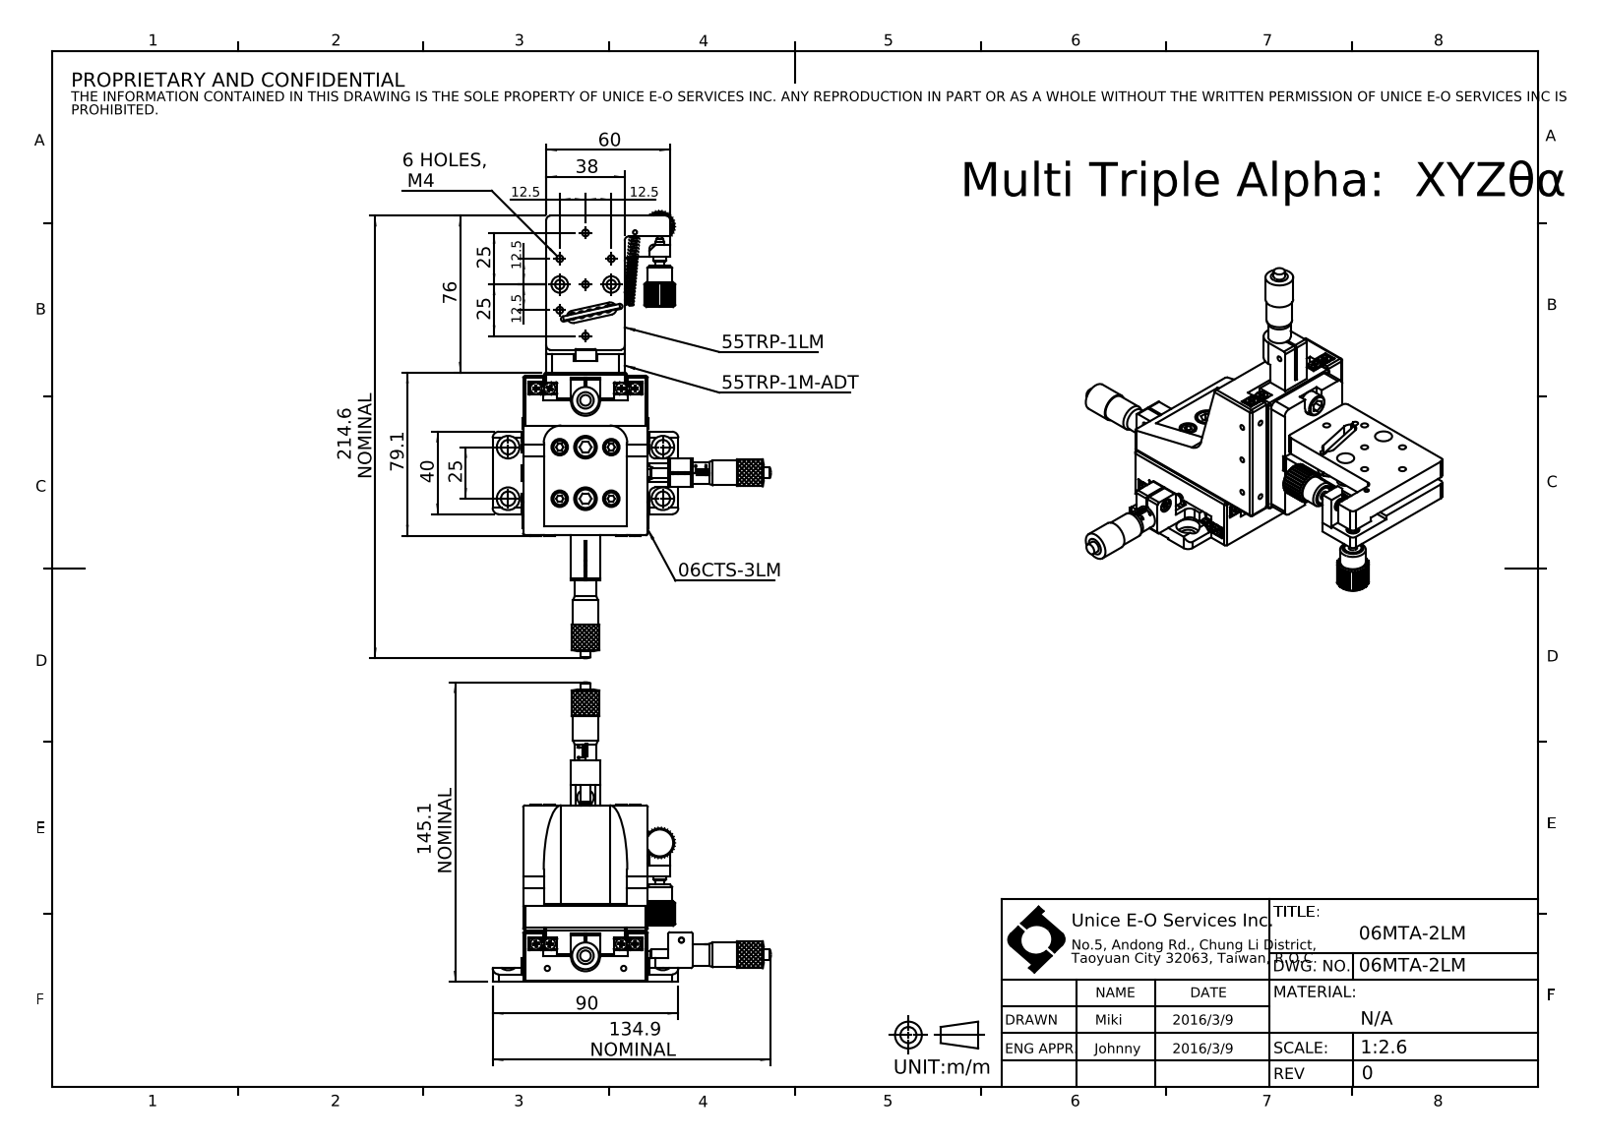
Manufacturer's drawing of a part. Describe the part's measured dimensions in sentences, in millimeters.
The part is named "06MTA-2LM". Its 3-D file was written by "SolidWorks 2016 (CONFIG_CONTROL_DESIGN)". It is 101 solids with 4854 faces: 2121 planar, 1262 cylindrical and 1471 other. Overall it measures 217.1 by 145.15 by 134.9 millimeters. Its volume is 294 998 cubic millimeters and its surface area 149 716 square millimeters. Round holes: 38 of diameter 2.05, 32 of diameter 5, 28 of diameter 2.5, 20 of diameter 3, 17 of diameter 3.3, 13 of diameter 8, 11 of diameter 4.5, 7 of diameter 1.6, 6 of diameter 11, 4 of diameter 6.6, 4 of diameter 7, 3 of diameter 3.4. Round bosses or shafts: 26 of diameter 3, 17 of diameter 5.5, 10 of diameter 4, 7 of diameter 7, 6 of diameter 6, 5 of diameter 12, 4 of diameter 10, 4 of diameter 2. Partial cylindrical surfaces (rounded edges, fillets, slot ends): 60 of radius 0.5, 48 of radius 1, 16 of radius 3, 12 of radius 3.1, 11 of radius 2, 8 of radius 0.75, 4 of radius 1.5, 2 of radius 1.25. The main face-to-face distances are 9, 6, 16.5, 3, 12, 10.7, 60.5, 4.7, 13.85, 57.85. The hole center spacings are 25, 12.5, 17.68, 8.62, 13.2, 20, 26.09, 30.2.
